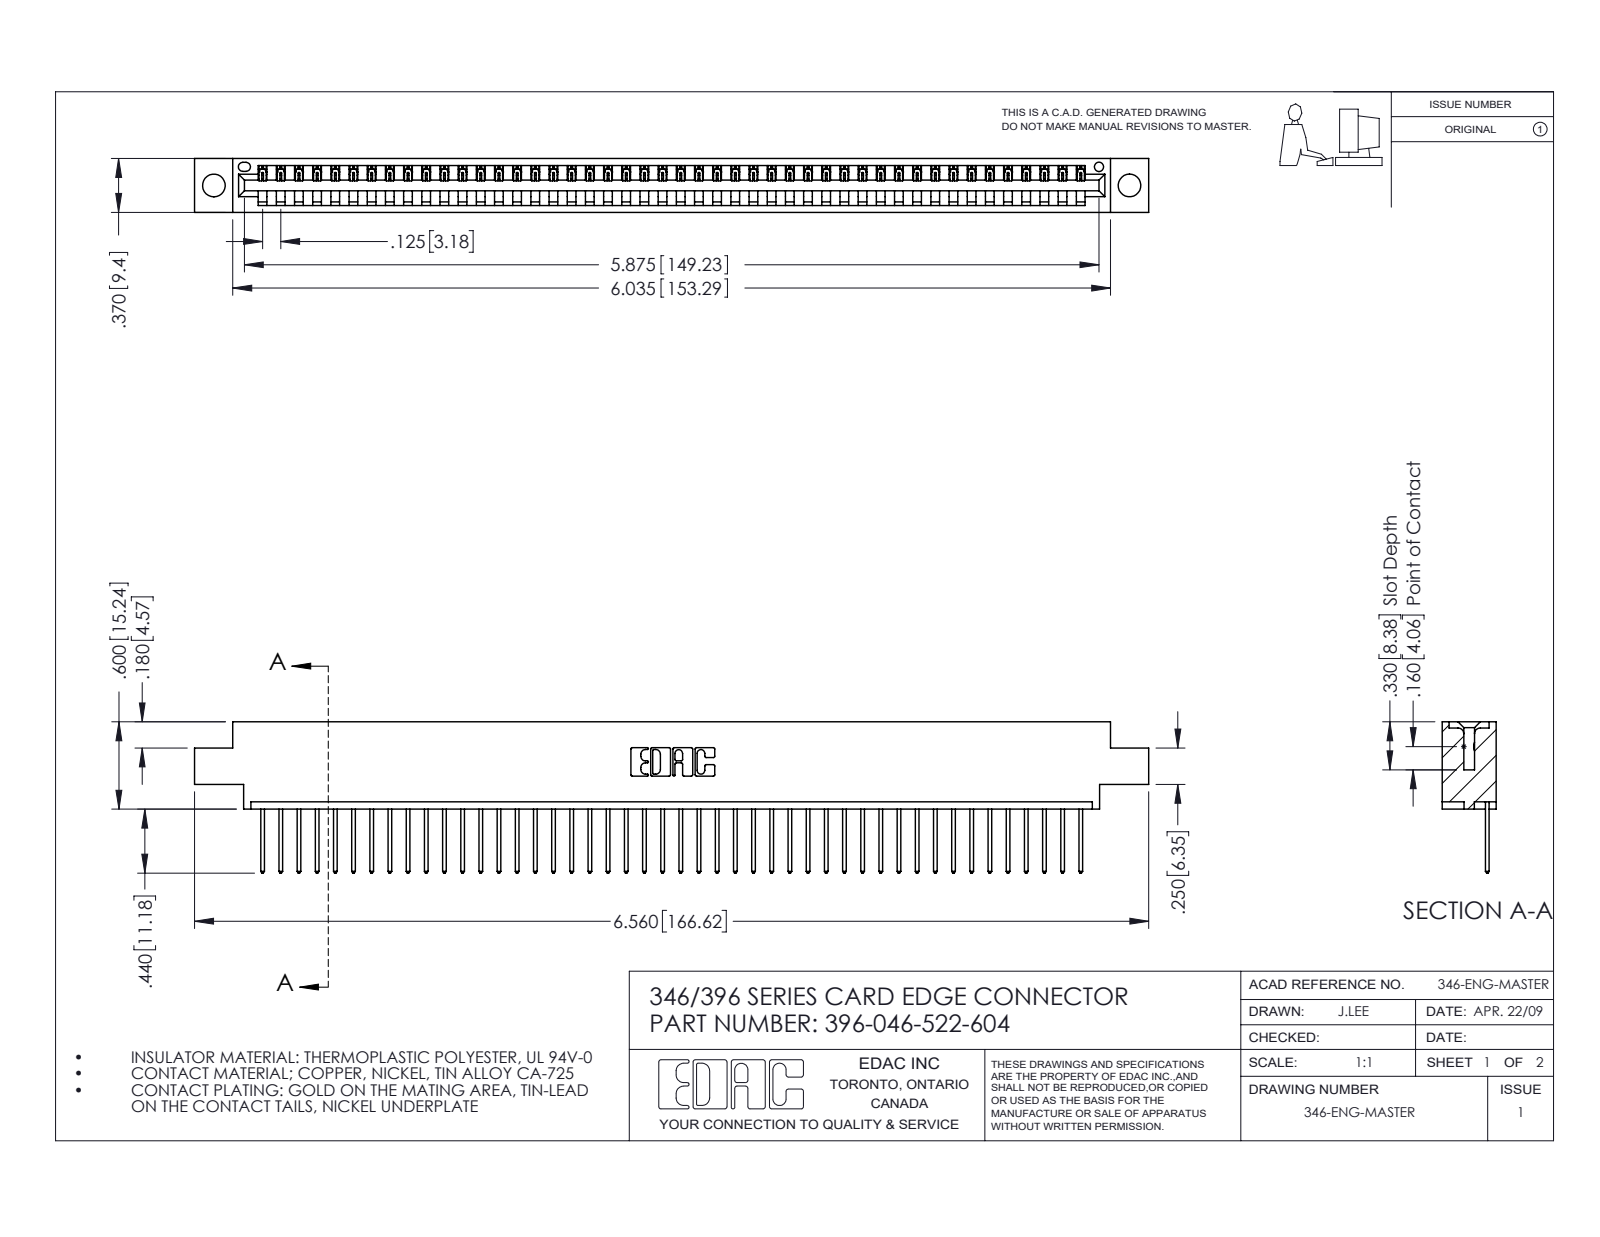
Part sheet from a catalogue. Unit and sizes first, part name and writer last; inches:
Units: inches
Overall size (bounding box): 6.56 × 1.04 × 0.37
Round holes (diameter × count): ⌀0.156 ×2, ⌀0.064 ×1
Partial cylindrical surfaces — rounded edges, fillets, slot ends (radius × count): R0.006 ×92, R0.01 ×92, R0.01 ×22, R0.007 ×6, R0.031 ×6, R0.026 ×3, R0.031 ×2, R0.04 ×2
Main face-to-face distances: 0.048, 0.322, 0.37, 0.25, 0.072, 0.298, 0.025, 0.148, 0.222, 0.1
Hole centre spacings: 0.246, 6.086, 6.295
Volume: 0.961 in³ · Surface area: 30.77 in²
Bodies: 47 solids, 2794 faces (1920 planar, 874 cylindrical, 0 other)
Part name (STEP PRODUCT): 346 Part_0.170 Offset - 0.156 Dia-TH; 345-292-001_345-293-122; 396-046-522-604
STEP written by: SolidWorks 2016 (CONFIG_CONTROL_DESIGN)
